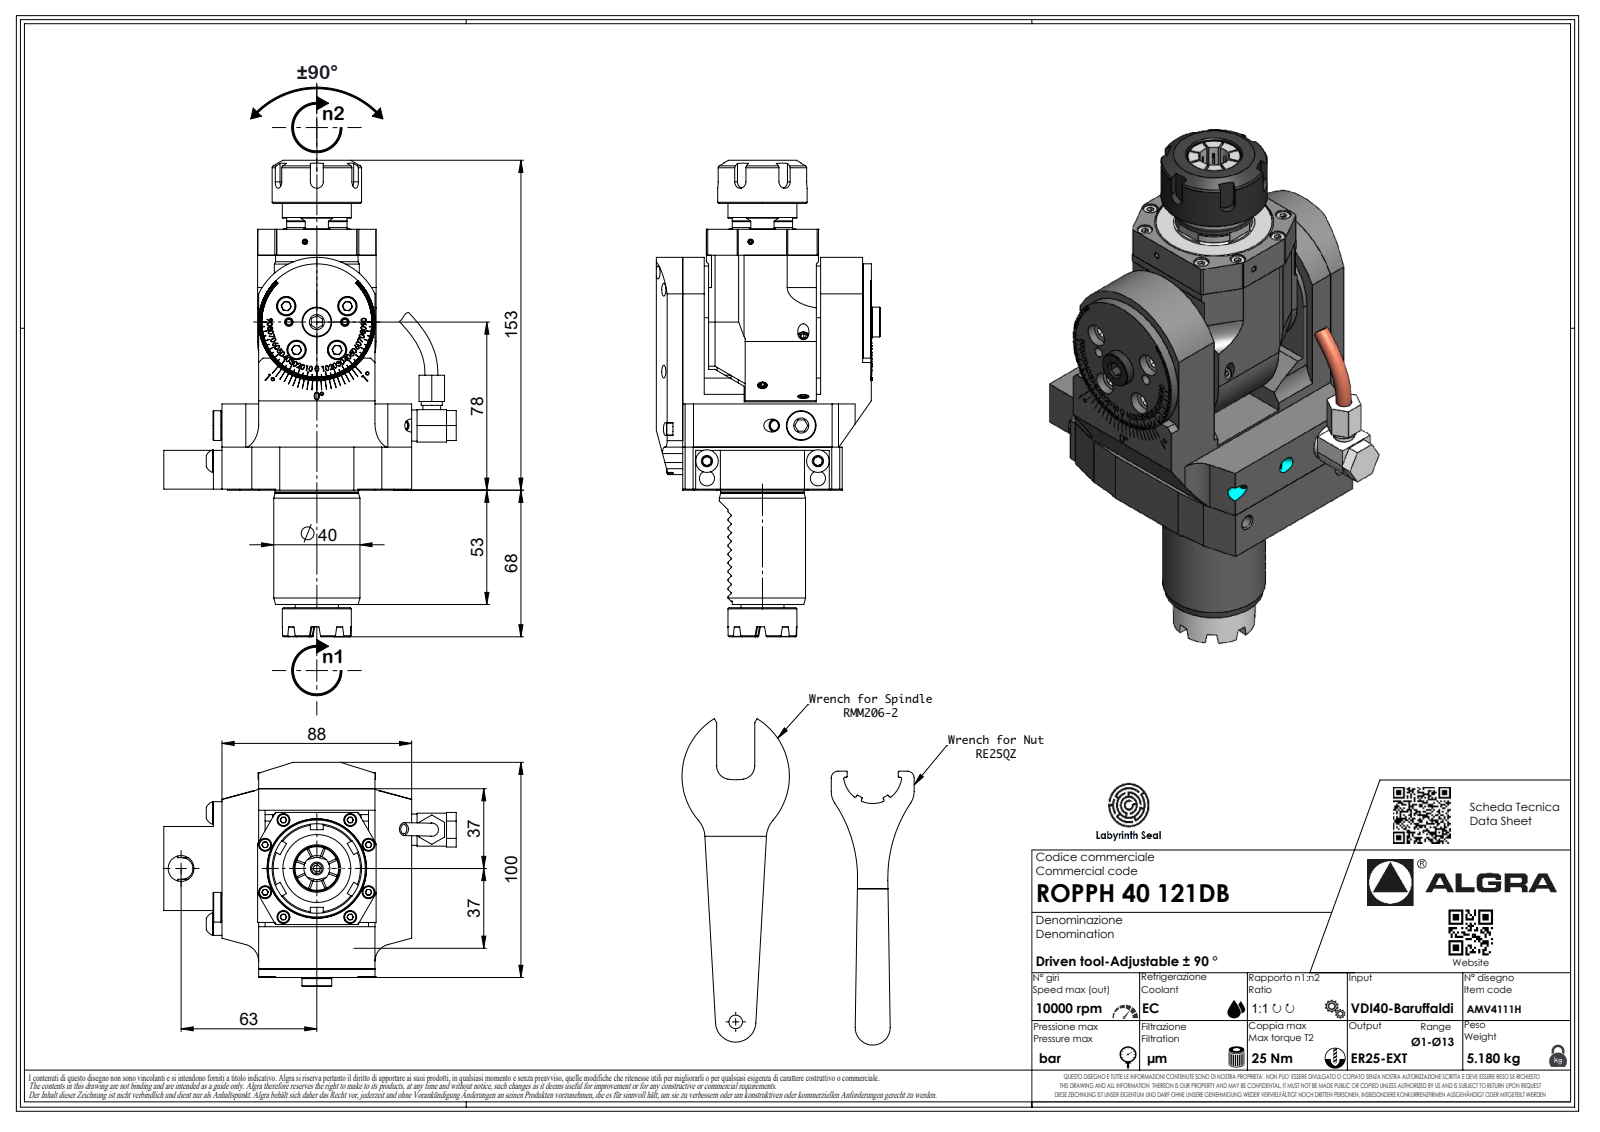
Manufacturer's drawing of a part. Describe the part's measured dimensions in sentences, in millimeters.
The part is named "ROPPH40121DB". Its 3-D file was written by "SolidWorks 2023 (AUTOMOTIVE_DESIGN)". It is 1 solid with 690 faces: 464 planar, 120 cylindrical and 106 other. Overall it measures 221.03 by 135.7 by 99.78 millimeters. Its volume is 762 175 cubic millimeters and its surface area 80 870 square millimeters. Round holes: 1 of diameter 3.15, 1 of diameter 17.2, 1 of diameter 46.2, 1 of diameter 52. Round bosses or shafts: 1 of diameter 54, 1 of diameter 47, 1 of diameter 46, 1 of diameter 41.5, 1 of diameter 40, 1 of diameter 38.7, 1 of diameter 32, 1 of diameter 20. Partial cylindrical surfaces (rounded edges, fillets, slot ends): 12 of radius 0.2, 11 of radius 0.3, 9 of radius 3, 8 of radius 1, 7 of radius 0.5, 7 of radius 0.78, 7 of radius 5.55, 2 of radius 2.5. The main face-to-face distances are 0.5, 17, 1, 71, 71.5, 54.5, 16.5, 54, 40, 39.5.
